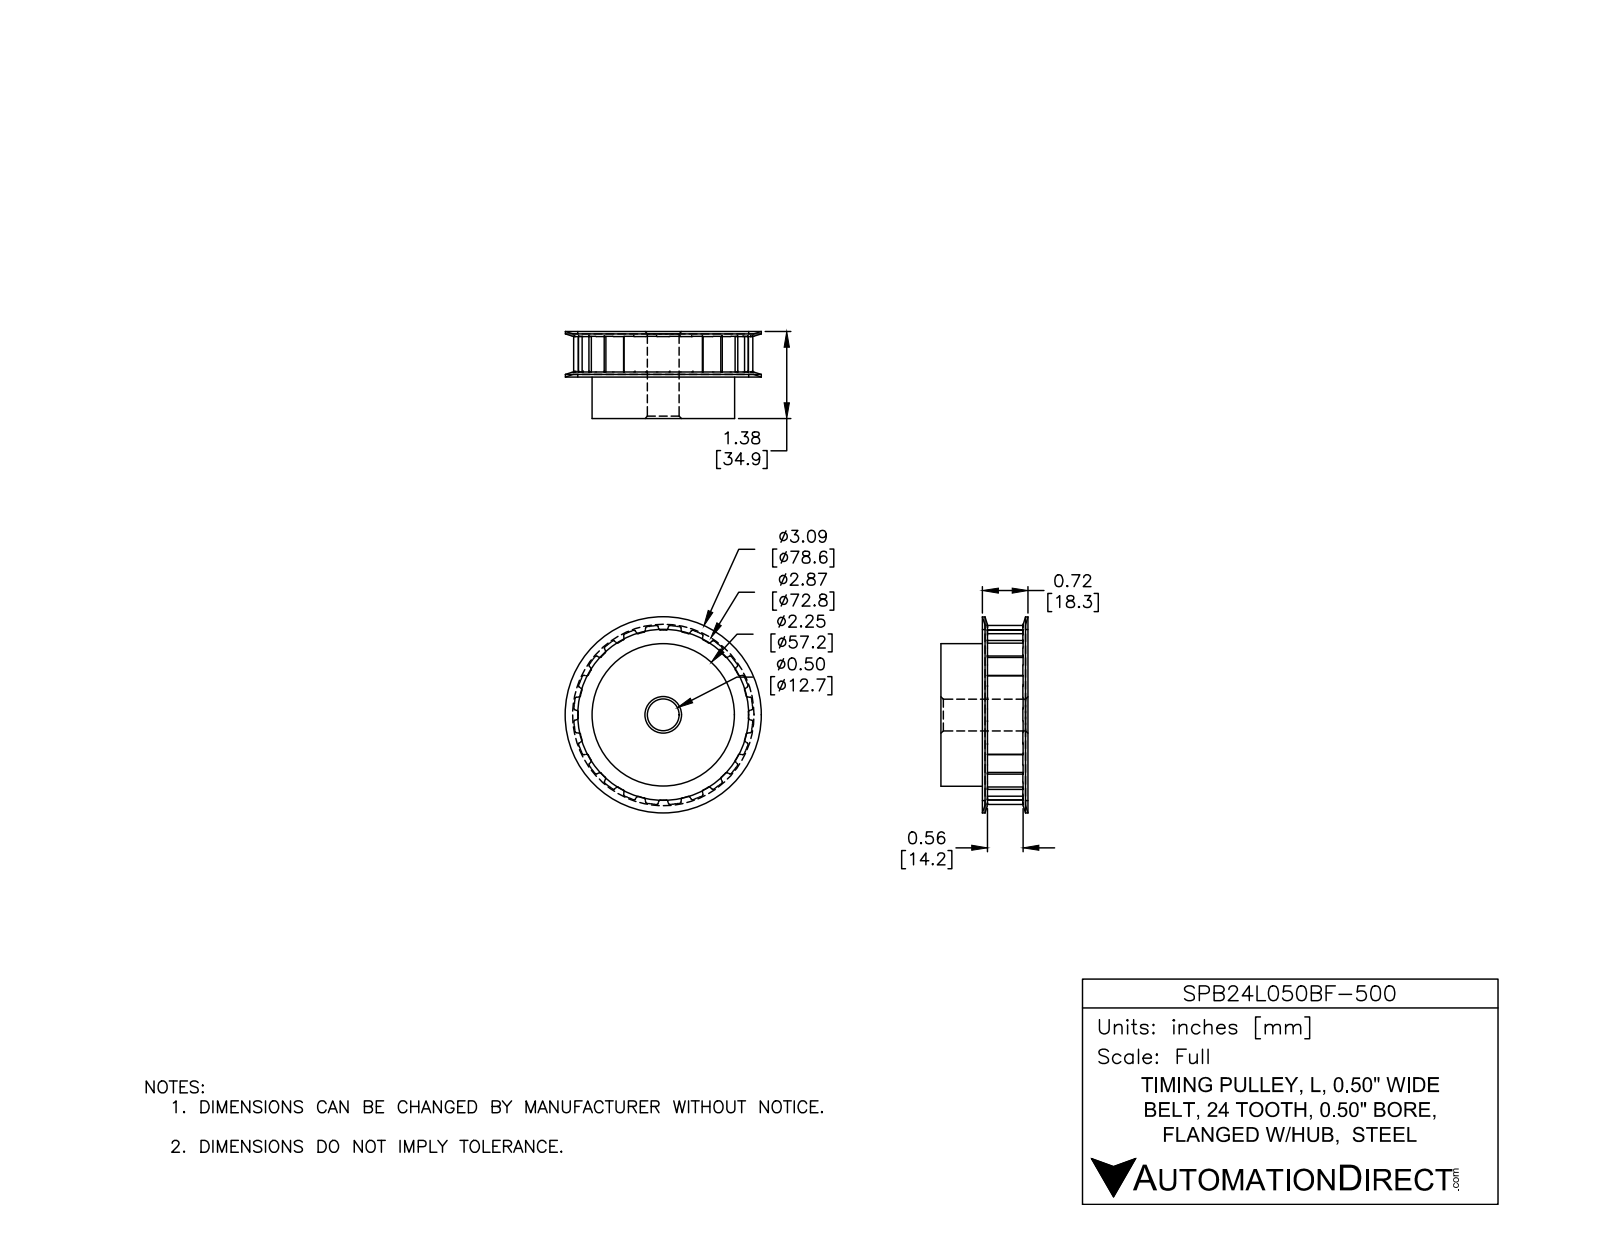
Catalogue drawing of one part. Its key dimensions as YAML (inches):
part_name: "SPB24L050BF-500"
step_written_by: "SolidWorks 2015 (AUTOMOTIVE_DESIGN)"
units: inches
bodies: {solids: 1, faces: 182, planar: 78, cylindrical: 86, other: 18}
overall_size: [3.094, 3.094, 1.375]
volume: 6.807
surface_area: 31.22
round_holes:
  - {diameter: 0.5, count: 1}
round_bosses_or_shafts:
  - {diameter: 2.25, count: 1}
partial_cylinders:
  - {radius: 0.015, count: 48}
  - {radius: 1.363, count: 1}
face_to_face_distances: [1.375, 0.71, 0.665, 0.04, 0.67, 1.335, 2.835, 2.835, 0.04, 0.63]
